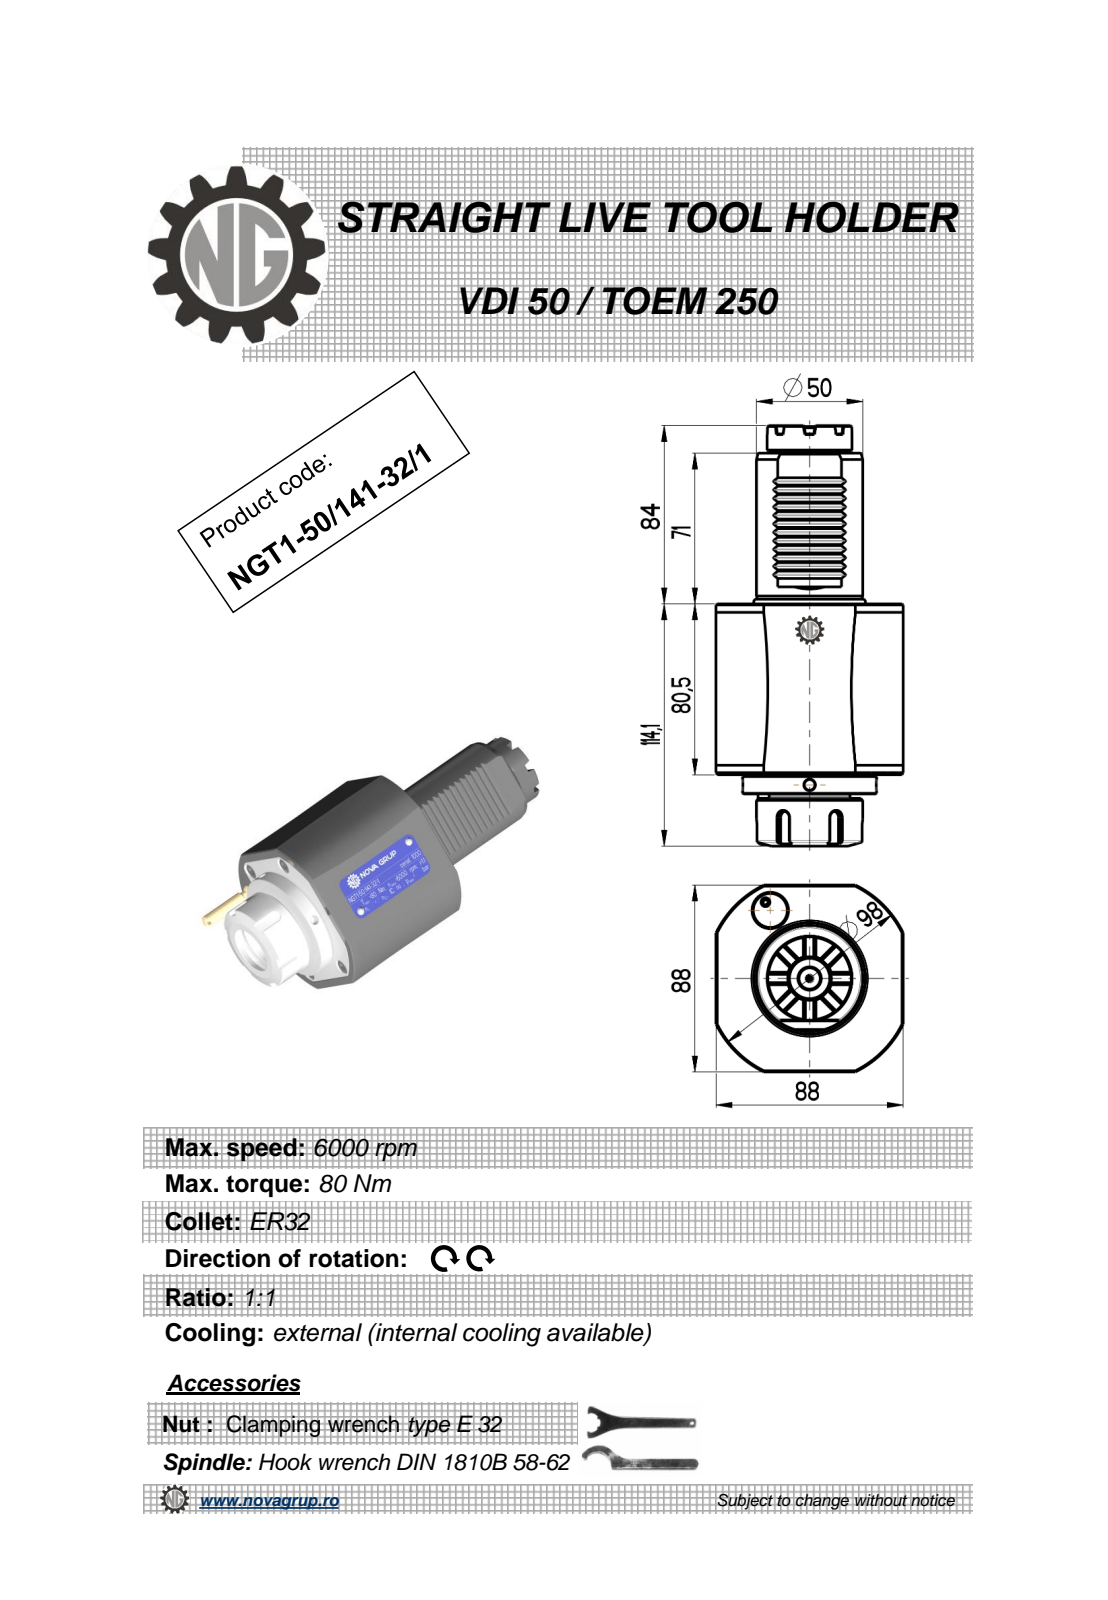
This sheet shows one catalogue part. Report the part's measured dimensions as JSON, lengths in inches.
{"part_name": "NGT1_50_141_32_1", "step_written_by": "PRO/ENGINEER BY PARAMETRIC TECHNOLOGY CORPORATION, 2010280 (CONFIG_CONTROL_DESIGN)", "units": "inches", "bodies": {"solids": 1, "faces": 352, "planar": 151, "cylindrical": 69, "other": 132}, "overall_size": [7.799, 3.465, 3.465], "volume_in3": 47.03, "surface_area_in2": 100.4, "round_holes": [[0.197, 2], [0.098, 1], [0.118, 1], [0.213, 1], [1.063, 1]], "round_bosses_or_shafts": [[2.48, 1], [2.012, 1], [1.969, 1], [1.614, 1], [1.575, 1], [0.787, 1], [0.354, 1], [0.276, 1]], "partial_cylinders_radius": [[0.012, 12], [0.118, 5], [0.404, 1], [1.929, 1]], "face_to_face_distances": [3.465, 3.169, 0.354, 3.524, 0.02, 6.319, 0.335, 3.189, 0.111, 2.795], "hole_center_spacings": [1.634]}
